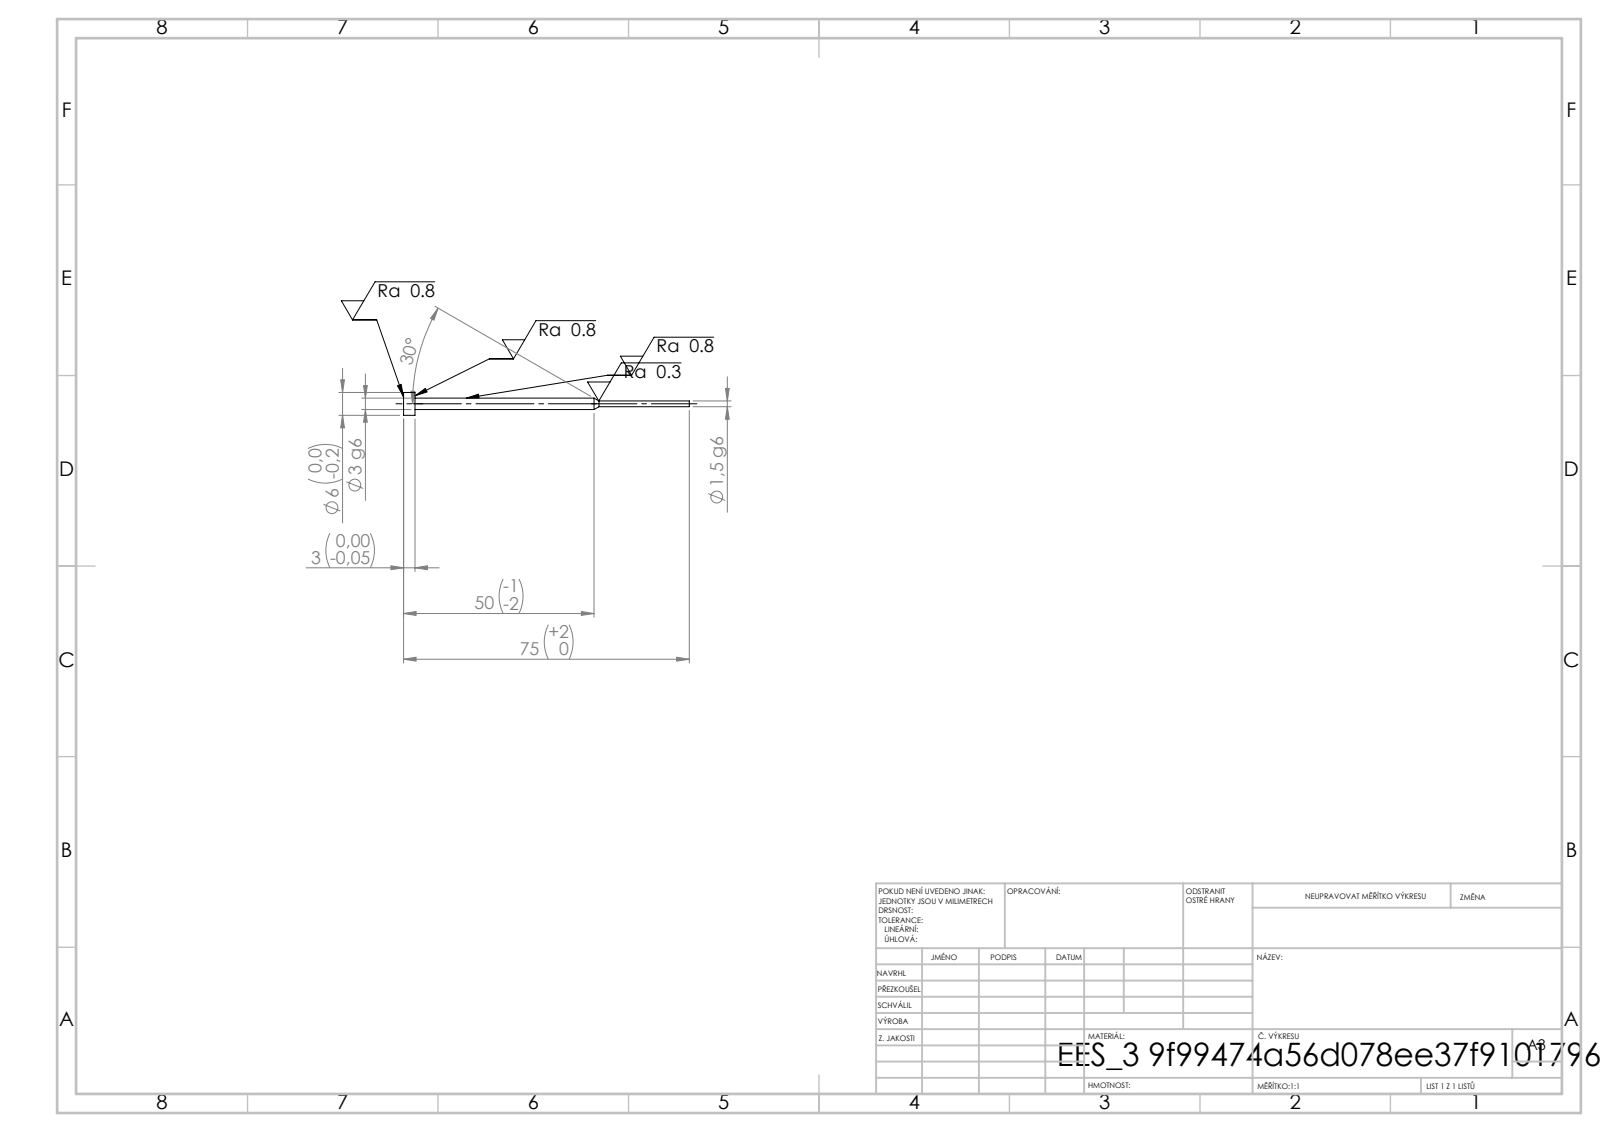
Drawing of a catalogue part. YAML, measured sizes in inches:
step_written_by: "SolidWorks 2019 (CONFIG_CONTROL_DESIGN)"
units: inches
bodies: {solids: 1, faces: 11, planar: 3, cylindrical: 6, other: 2}
overall_size: [2.953, 0.236, 0.236]
volume: 0.028
surface_area: 1.04
round_bosses_or_shafts:
  - {diameter: 0.236, count: 1}
  - {diameter: 0.118, count: 1}
  - {diameter: 0.059, count: 1}
face_to_face_distances: [0.118, 2.835, 2.953]
